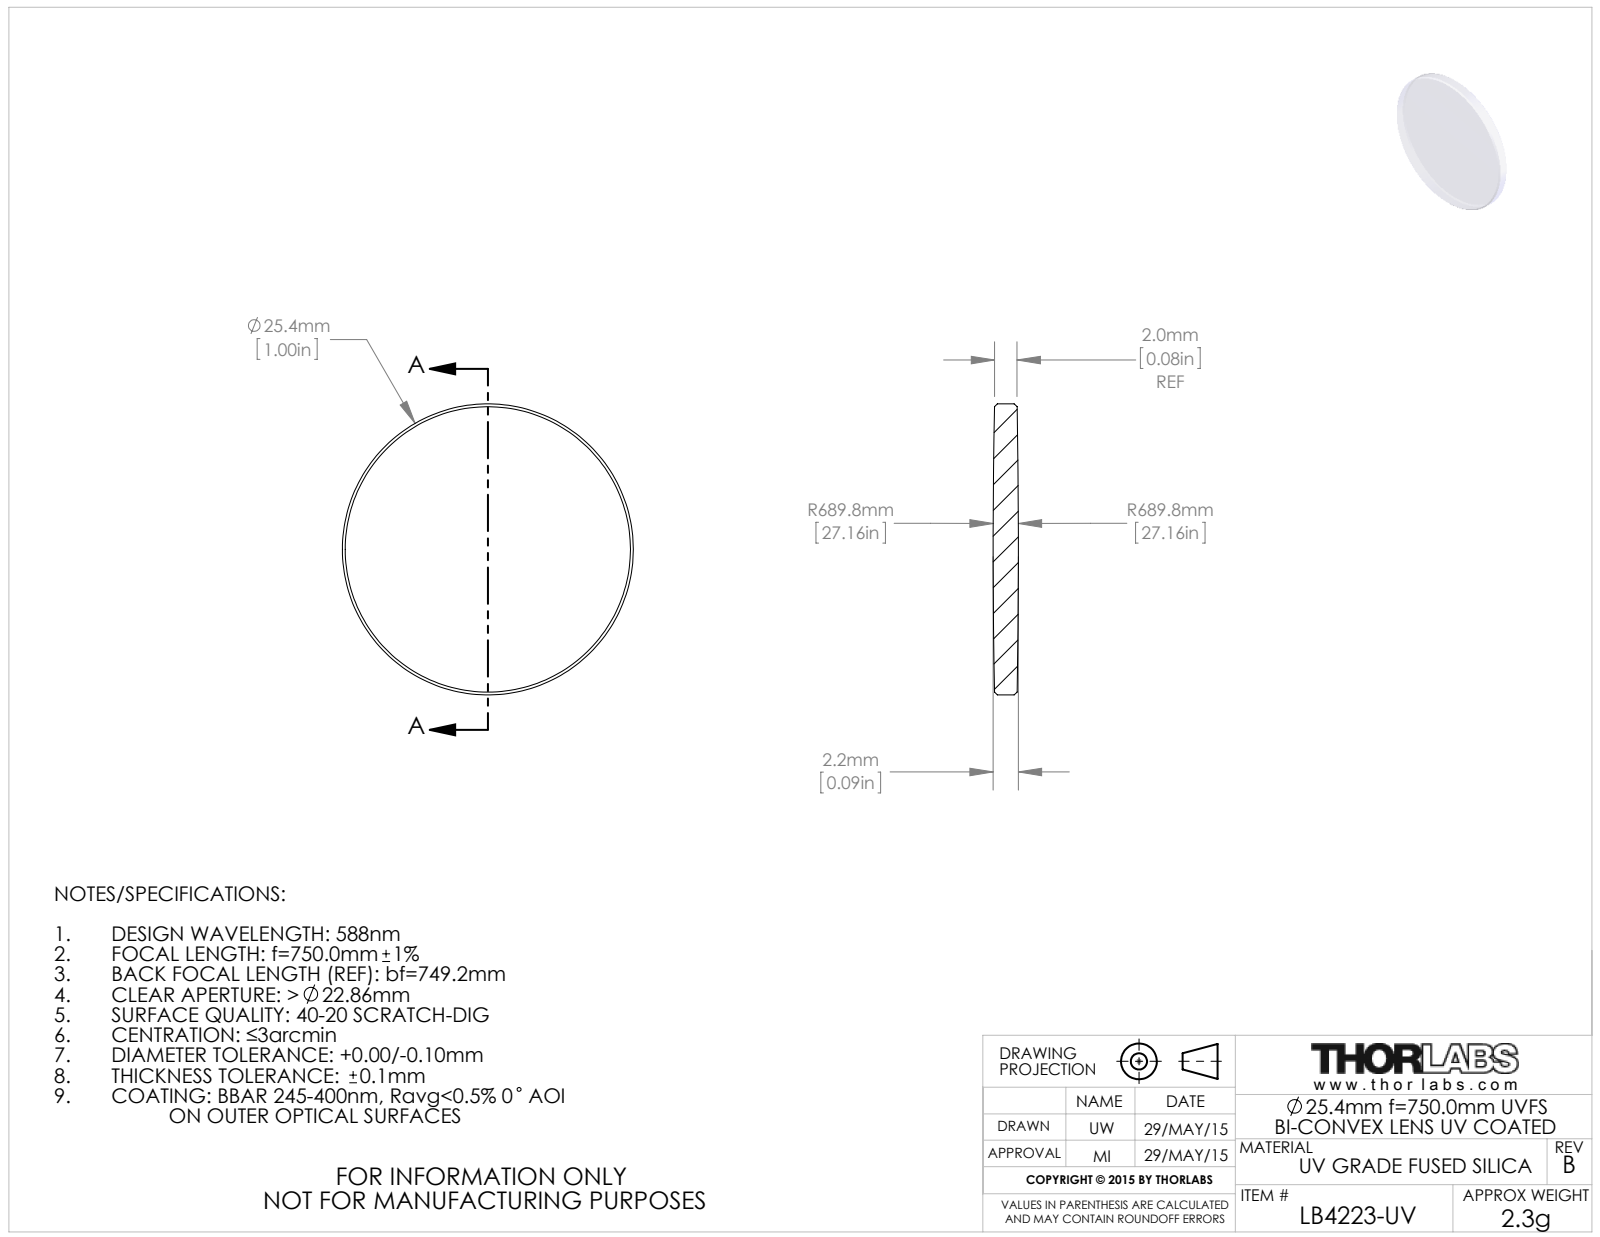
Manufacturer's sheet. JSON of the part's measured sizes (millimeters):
{"part_name": "4329-E0W", "step_written_by": "SolidWorks 2014 (CONFIG_CONTROL_DESIGN)", "units": "millimeters", "bodies": {"solids": 1, "faces": 10, "planar": 0, "cylindrical": 2, "other": 8}, "overall_size": [25.4, 25.4, 2.2], "volume_mm3": 1051, "surface_area_mm2": 1147, "round_bosses_or_shafts": [[25.4, 1]]}
